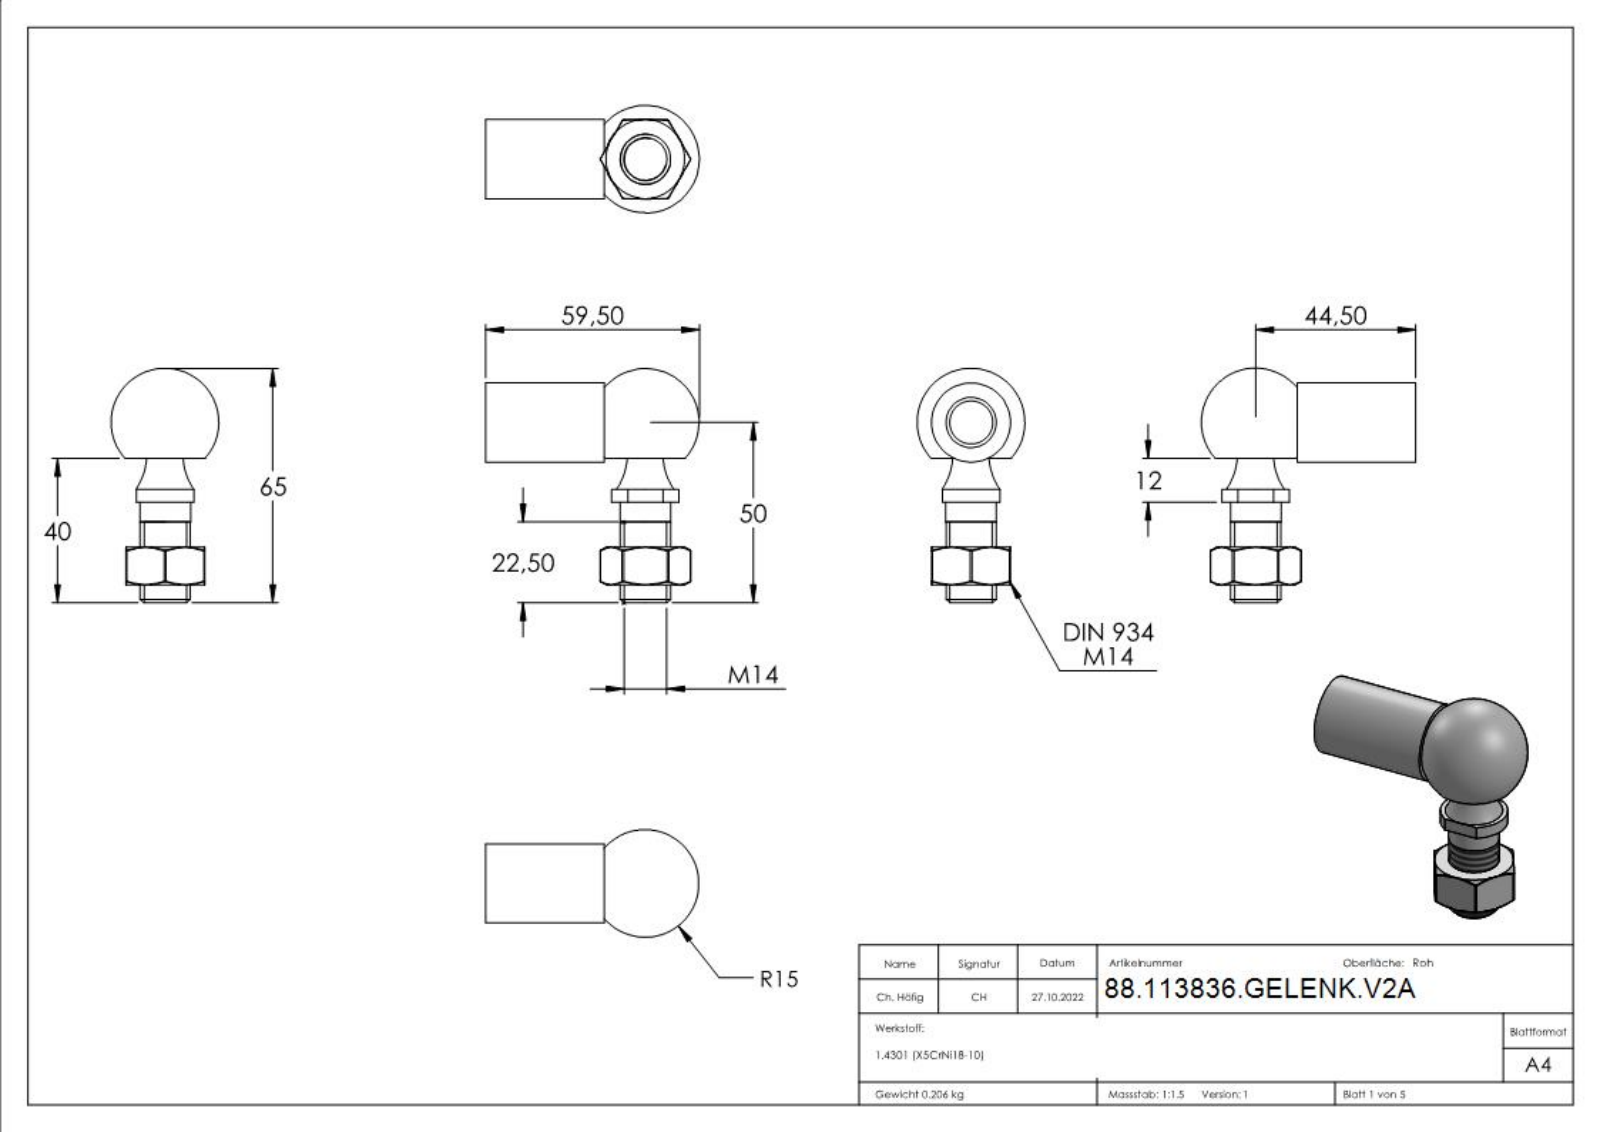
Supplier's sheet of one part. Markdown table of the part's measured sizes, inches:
| quantity | value |
| --- | --- |
| part name | 3836-GELENK Teil1_3836-GELENK-V2A Teil1; 3836-GELENK Teil4_3836-GELENK-V2A Teil4; 3836-GELENK-V2A; 3836-GELENK Teil2_3836-GELENK-V2A Teil2 |
| STEP written by | SolidWorks 2018 (CONFIG_CONTROL_DESIGN) |
| units | inches |
| bodies | 3 solids, 456 faces (223 planar, 15 cylindrical, 218 other) |
| overall size | 2.567 × 2.343 × 1.181 |
| volume | 1.592 in³ |
| surface area | 20.69 in² |
| round holes (diameter × count) | 0.472 × 2, 0.768 × 1 |
| round bosses / shafts (diameter × count) | 0.88 × 1, 0.866 × 1, 0.555 × 1, 0.551 × 1 |
| partial cylindrical surfaces (radius × count) | 0.02 × 6, 0.37 × 1 |
| main face-to-face distances | 0.866, 0.413, 1.299, 0.197, 0.61, 1.104, 0.907, 0.494, 1.583, 1.386 |
